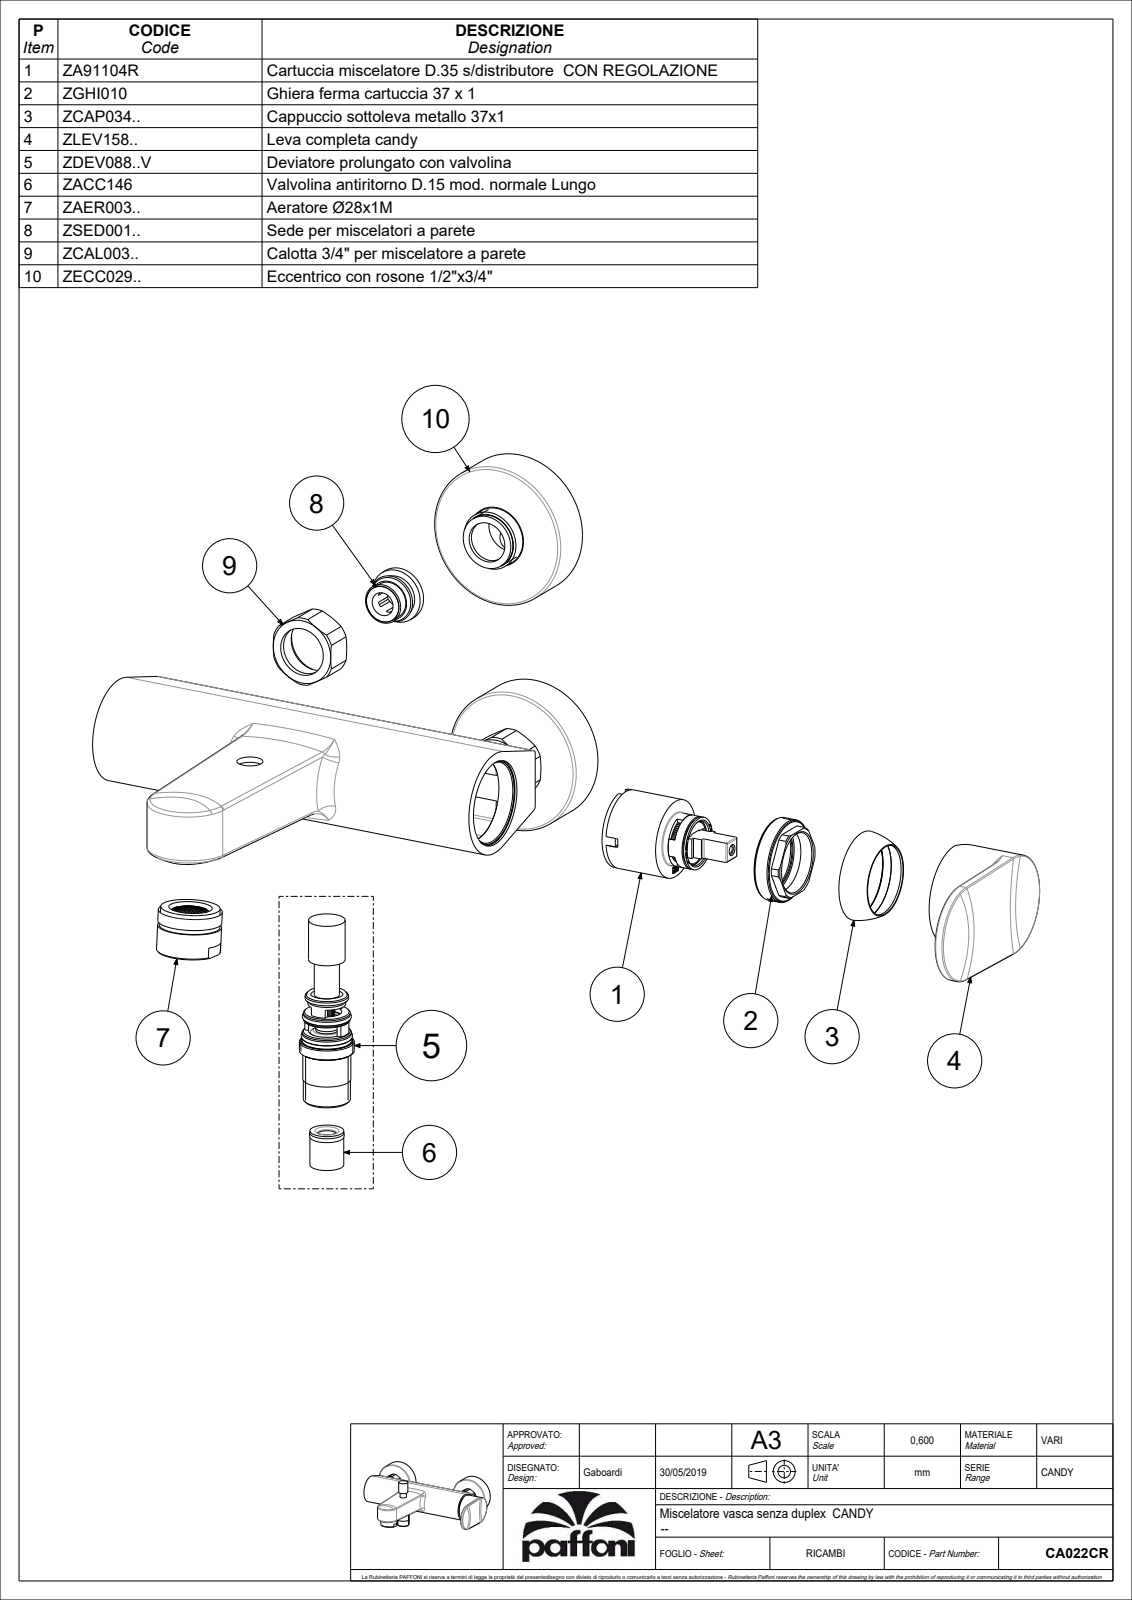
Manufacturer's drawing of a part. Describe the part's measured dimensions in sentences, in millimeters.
The part is named "CA022CR". Its 3-D file was written by "CREO PARAMETRIC BY PTC INC, 2020044 (CONFIG_CONTROL_DESIGN)". It is 5 solids with 2225 faces: 1627 planar, 269 cylindrical and 329 other. Overall it measures 234.35 by 191.5 by 77.55 millimeters. Its volume is 384 644 cubic millimeters and its surface area 155 916 square millimeters. Round holes: 2 of diameter 16.5, 2 of diameter 19, 2 of diameter 22, 2 of diameter 28.5, 1 of diameter 3, 1 of diameter 3.5, 1 of diameter 4.5, 1 of diameter 5, 1 of diameter 10, 1 of diameter 11, 1 of diameter 12.8, 1 of diameter 13. Round bosses or shafts: 2 of diameter 63.5, 1 of diameter 45, 1 of diameter 28, 1 of diameter 26.5, 1 of diameter 22, 1 of diameter 21.5, 1 of diameter 21, 1 of diameter 20.8. Partial cylindrical surfaces (rounded edges, fillets, slot ends): 91 of radius 1, 4 of radius 3, 2 of radius 1.5, 2 of radius 15.5, 1 of radius 3.5, 1 of radius 9, 1 of radius 9.75, 1 of radius 14.46. The main face-to-face distances are 3.5, 20, 14.5, 34.5, 3, 5, 18, 0.5, 17, 38. The hole center spacings are 6, 39.6, 150, 189.6.
